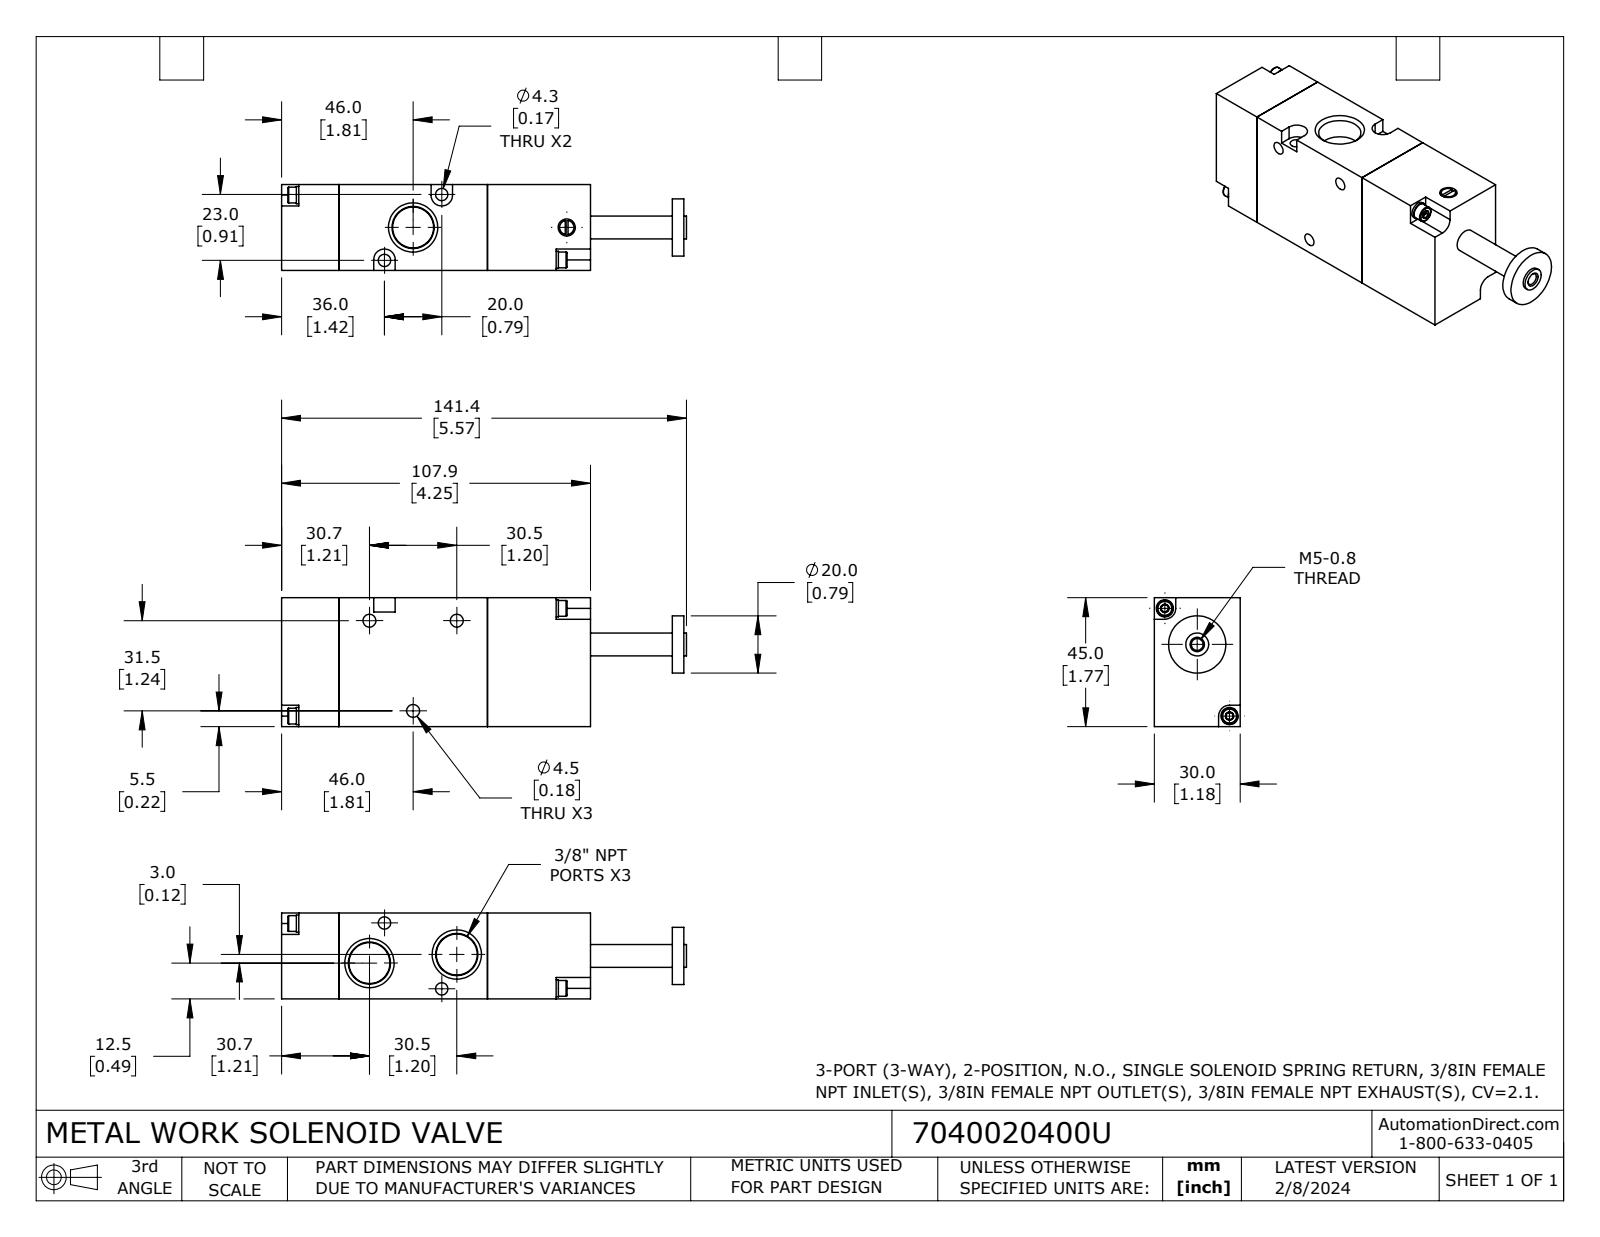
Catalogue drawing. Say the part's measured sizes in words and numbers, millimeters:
The part is named "7040020400U". Its 3-D file was written by "SolidWorks 2023 (CONFIG_CONTROL_DESIGN)". It is 11 solids with 247 faces: 116 planar, 61 cylindrical and 70 other. Overall it measures 141.4 by 45 by 30 millimeters. Its volume is 139 900 cubic millimeters and its surface area 30 280 square millimeters. Round holes: 4 of diameter 3, 3 of diameter 4.5, 2 of diameter 4.3, 1 of diameter 4.1, 1 of diameter 6. Round bosses or shafts: 4 of diameter 6, 4 of diameter 5.5, 1 of diameter 20, 1 of diameter 8, 1 of diameter 5. Partial cylindrical surfaces (rounded edges, fillets, slot ends): 4 of radius 3.8, 2 of radius 3.8. The main face-to-face distances are 30, 51.9, 45, 20, 71.9, 36, 107.9, 87.9, 37, 8. The hole center spacings are 16.9, 22.6, 27.4, 35, 37.6, 43.9, 30.5, 30.5.
